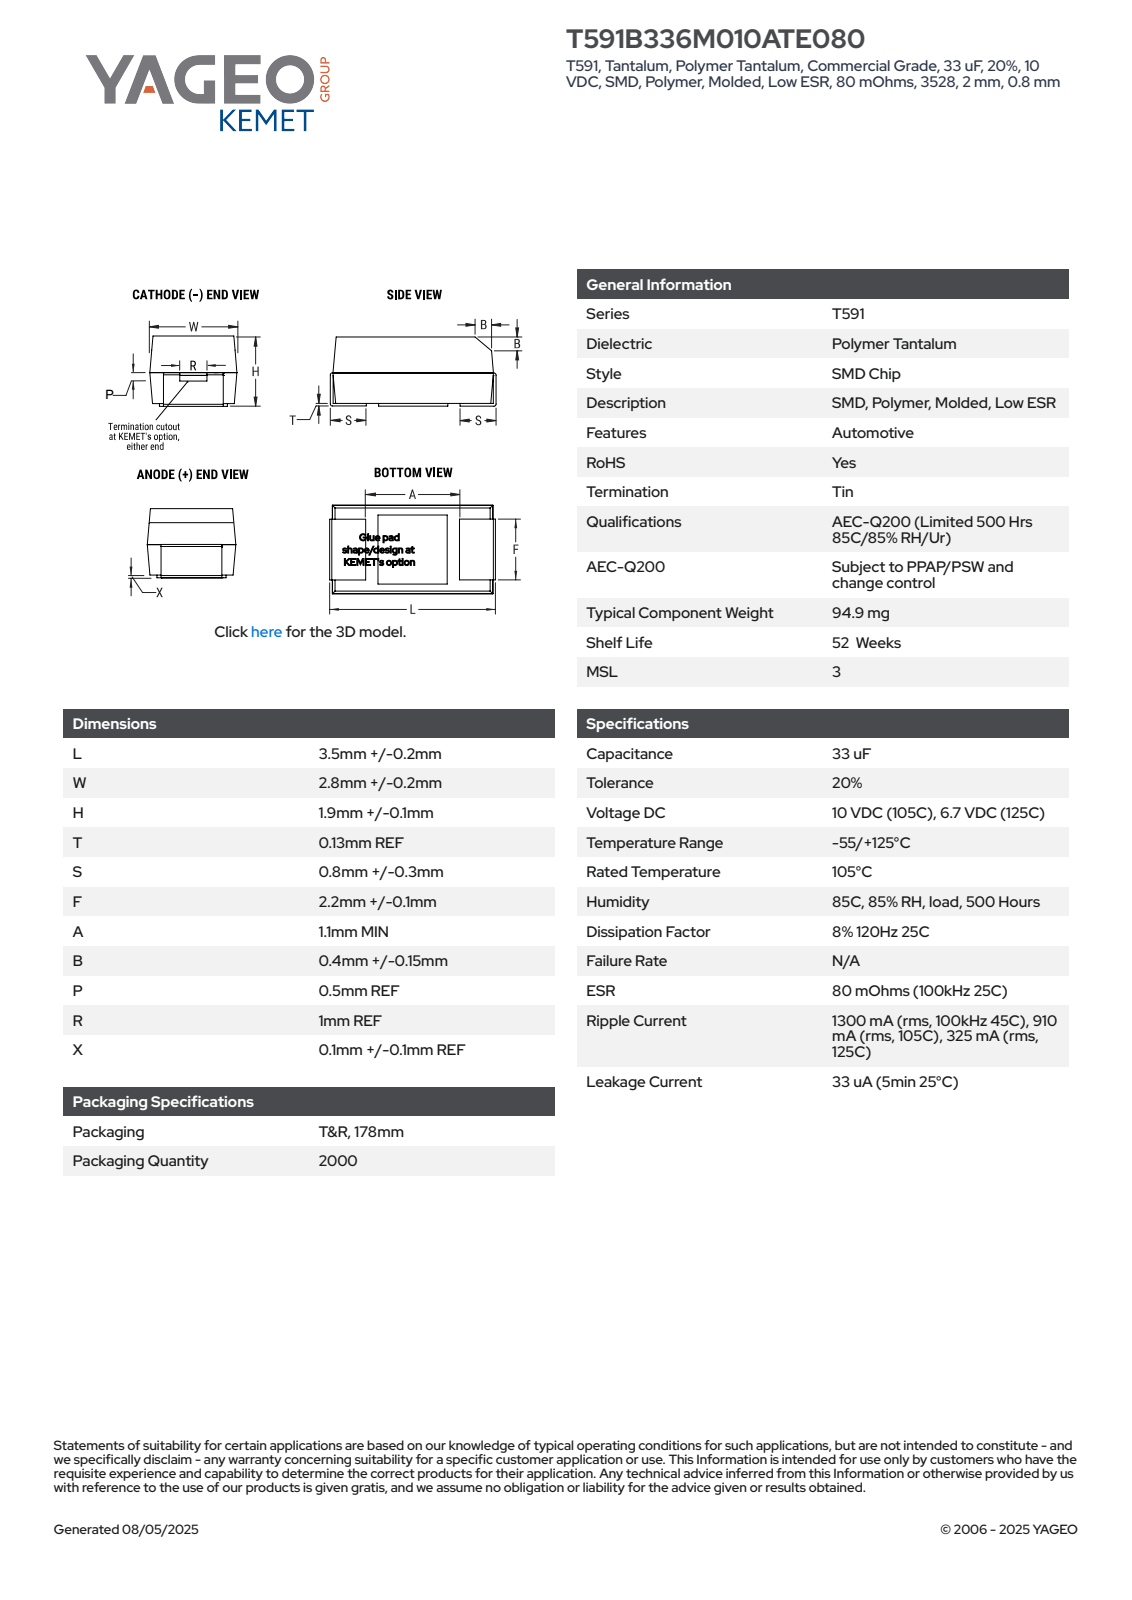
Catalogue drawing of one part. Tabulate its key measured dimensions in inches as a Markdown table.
| quantity | value |
| --- | --- |
| part name | CTSM_TCM2NKKO_3528_L3.7W3H2T0.13S0.8F2.3A1.1B0.55P0.5R1X0.1 |
| STEP written by | SolidWorks 2021 (AUTOMOTIVE_DESIGN) |
| units | inches |
| bodies | 4 solids, 100 faces (95 planar, 5 cylindrical, 0 other) |
| overall size | 0.146 × 0.118 × 0.08 |
| volume | 0.001 in³ |
| surface area | 0.079 in² |
| partial cylindrical surfaces (radius × count) | 0.004 × 4 |
| main face-to-face distances | 0.117, 0.079, 0.08, 0.075, 0.141, 0.146, 0.135, 0.015, 0.026, 0.031 |
